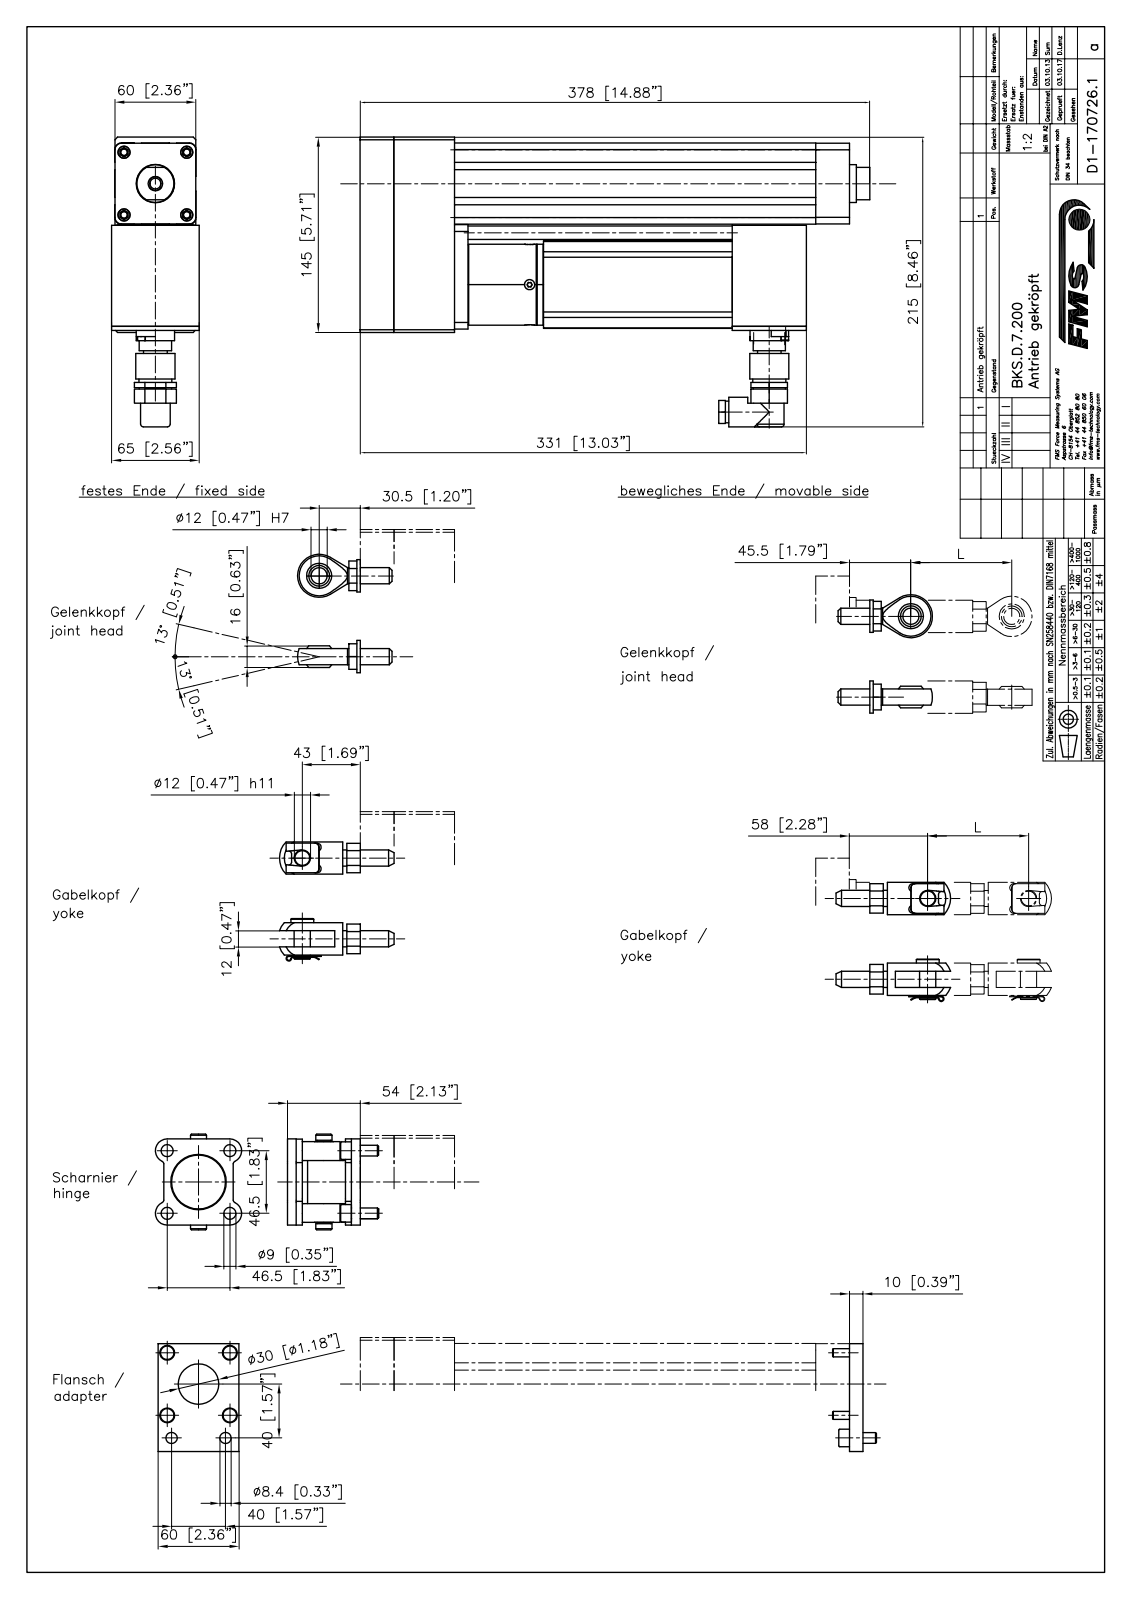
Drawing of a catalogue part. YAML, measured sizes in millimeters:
part_name: "K1707261_STP; K1309121; K0702222; K0804232 (+8 more)"
step_written_by: "Mechanical Desktop 2009 (CONFIG_CONTROL_DESIGN)"
units: millimeters
bodies: {solids: 43, faces: 1230, planar: 463, cylindrical: 514, other: 253}
overall_size: [471, 215, 65]
volume: 1786000
surface_area: 469171
round_holes:
  - {diameter: 3.42, count: 8}
  - {diameter: 5.15, count: 8}
  - {diameter: 5.5, count: 8}
  - {diameter: 2.6, count: 6}
  - {diameter: 10, count: 5}
  - {diameter: 3.4, count: 4}
  - {diameter: 4.2, count: 4}
  - {diameter: 4.5, count: 4}
  - {diameter: 5.3, count: 4}
  - {diameter: 6.3, count: 4}
  - {diameter: 6.4, count: 4}
  - {diameter: 6.65, count: 4}
round_bosses_or_shafts:
  - {diameter: 8, count: 8}
  - {diameter: 6, count: 8}
  - {diameter: 5, count: 8}
  - {diameter: 2.15, count: 7}
  - {diameter: 3, count: 6}
  - {diameter: 10, count: 5}
  - {diameter: 7, count: 4}
  - {diameter: 4, count: 4}
partial_cylinders:
  - {radius: 5, count: 19}
  - {radius: 0.5, count: 14}
  - {radius: 0.4, count: 12}
  - {radius: 0.69, count: 12}
  - {radius: 3, count: 8}
  - {radius: 4.5, count: 8}
  - {radius: 2, count: 6}
  - {radius: 20, count: 5}
face_to_face_distances: [60.15, 2.5, 55, 62.5, 60.3, 2.35, 62.65, 1.5, 70, 65]
hole_center_spacings: [18.46, 23.68, 38.85, 42.56, 54.86, 13.31, 20, 26]
